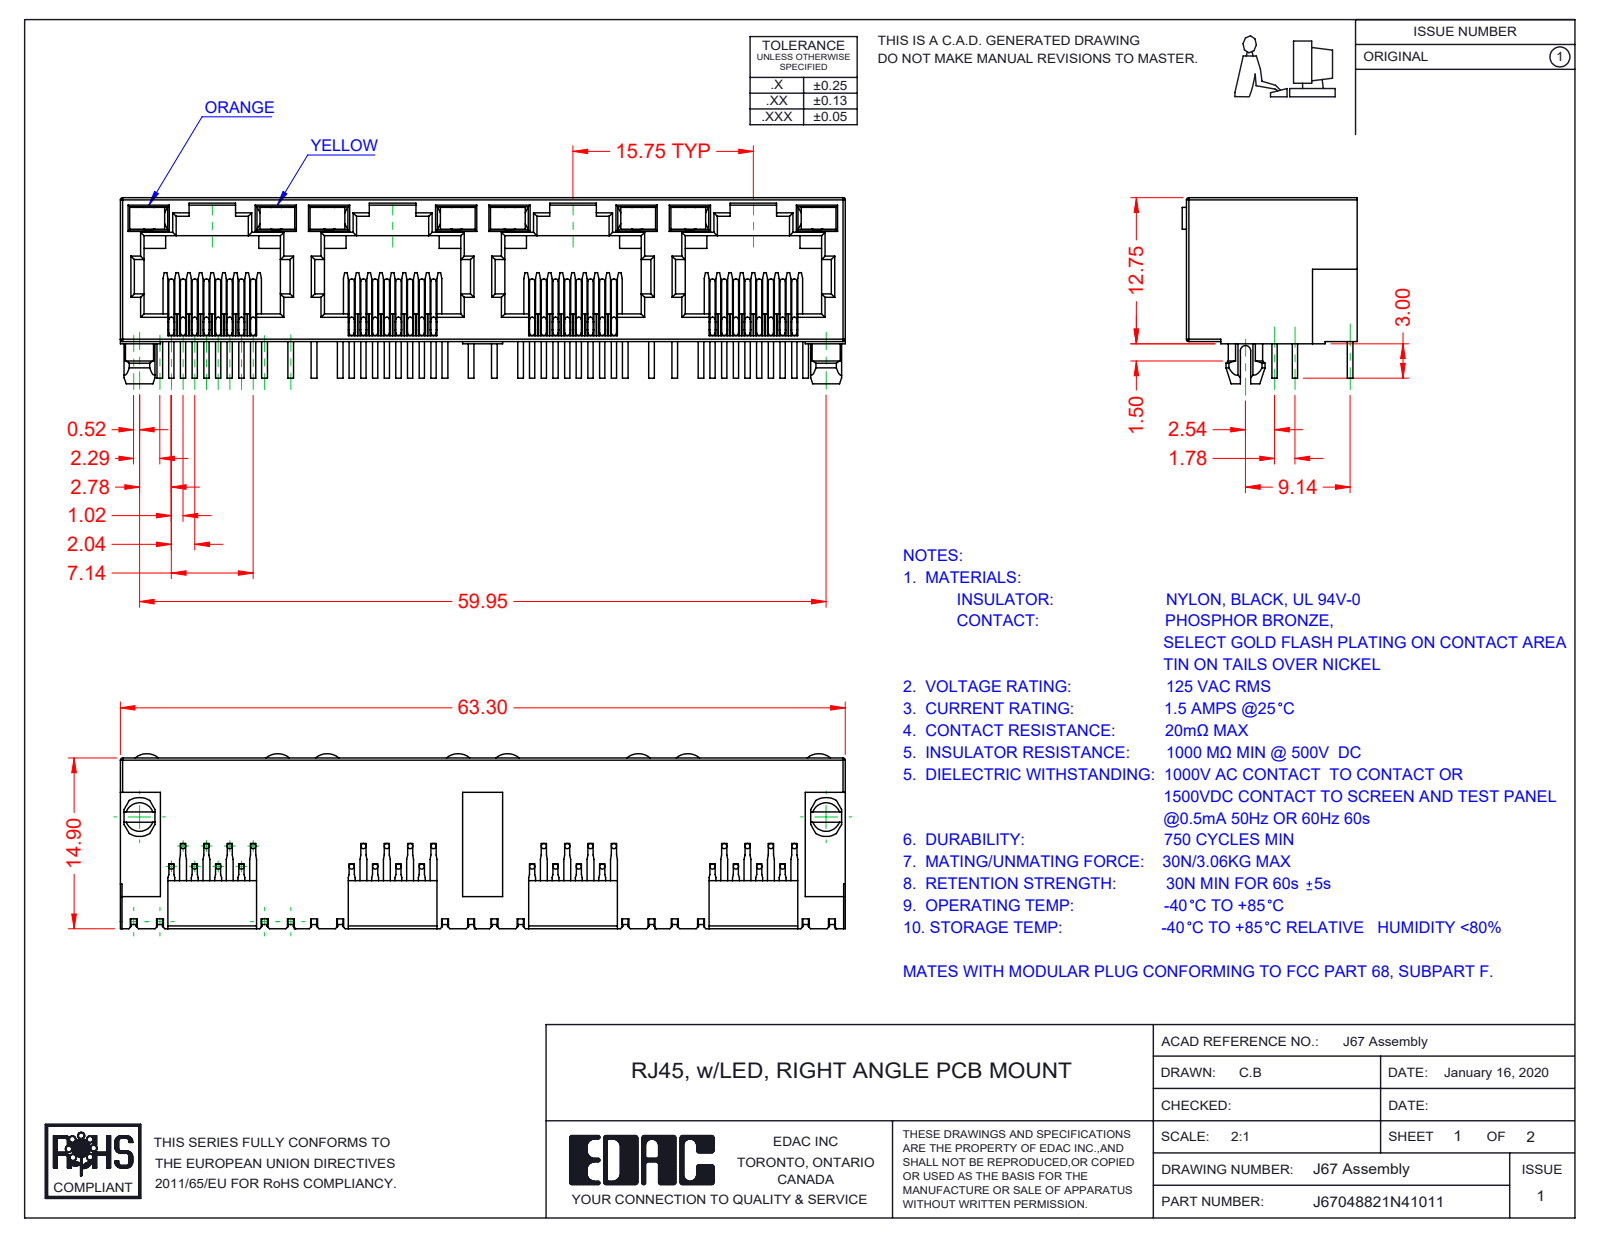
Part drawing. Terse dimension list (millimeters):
name: 67 LED LH_4-Orange; 67 Contacts; 67 LED RH_1-Yellow; 67 Insulator (+1 more)
written by: SolidWorks 2016 (CONFIG_CONTROL_DESIGN)
unit: mm
bodies: 41 solids, 2465 faces (1781 planar, 476 cylindrical, 208 other)
size: 63.3 × 16.25 × 15.28
volume: 5 159 mm³; area: 11 573 mm²
bosses: 96× ⌀0.46
rounds: 66× R0.2, 29× R0.3, 9× R0.45, 8× R1.55, 2× R1.5, 2× R1.7, 1× R0.35, 1× R1
face distances: 0.5, 12.55, 1.89, 0.89, 10, 15.75, 1, 1.39, 11, 11.89
